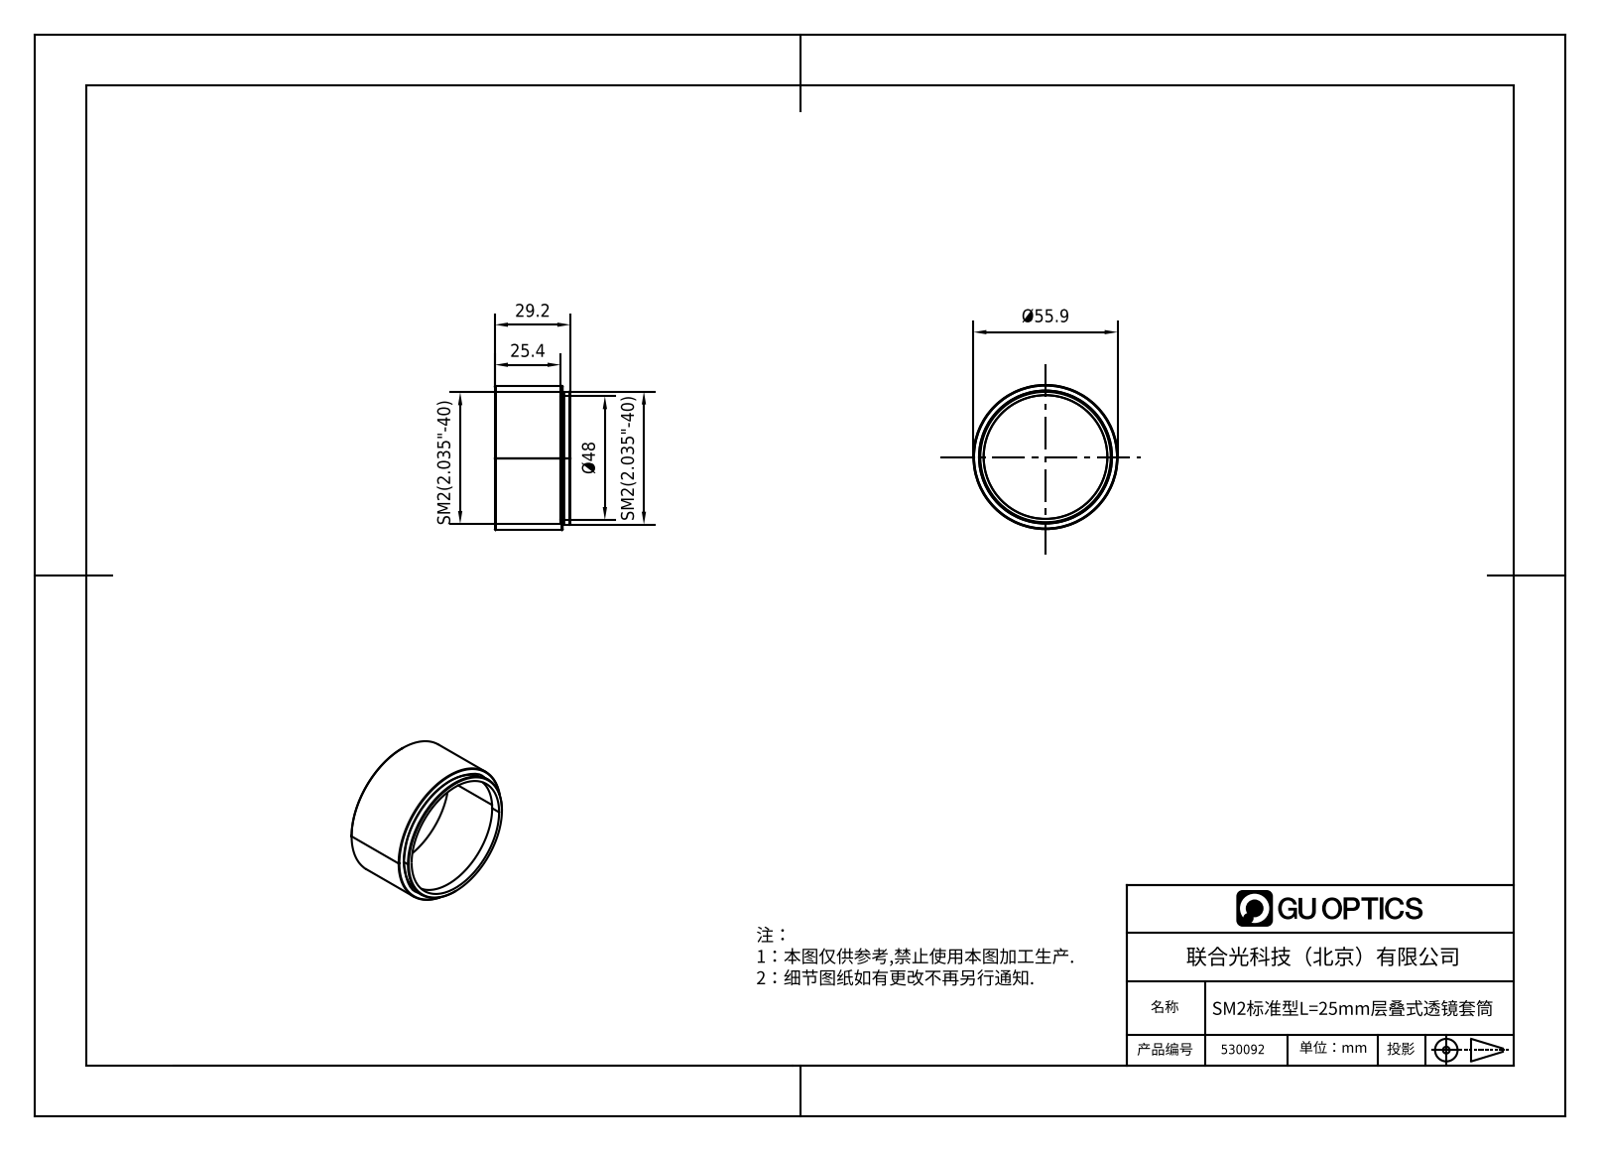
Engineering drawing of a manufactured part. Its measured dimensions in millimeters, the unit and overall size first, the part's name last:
Units: millimetres
Overall size (bounding box): 55.9 × 55.9 × 29.2
Round holes (diameter × count): ⌀47.69 ×1, ⌀48 ×1, ⌀51.05 ×1
Round bosses / shafts (diameter × count): ⌀55.9 ×1, ⌀51.6 ×1, ⌀50.6 ×1
Main face-to-face distances: 26.2, 3, 29.2, 25.4, 0.8, 3.8, 22.4, 23.2, 0.5, 2.5
Bodies: 0 solids, 36 faces (13 planar, 12 cylindrical, 11 other)
Part name (STEP PRODUCT): 1.7.1.18_ZTC-2-1.0_SM2标准型1.0英寸层叠式透镜套筒
STEP written by: SolidWorks 2018 (AUTOMOTIVE_DESIGN)
